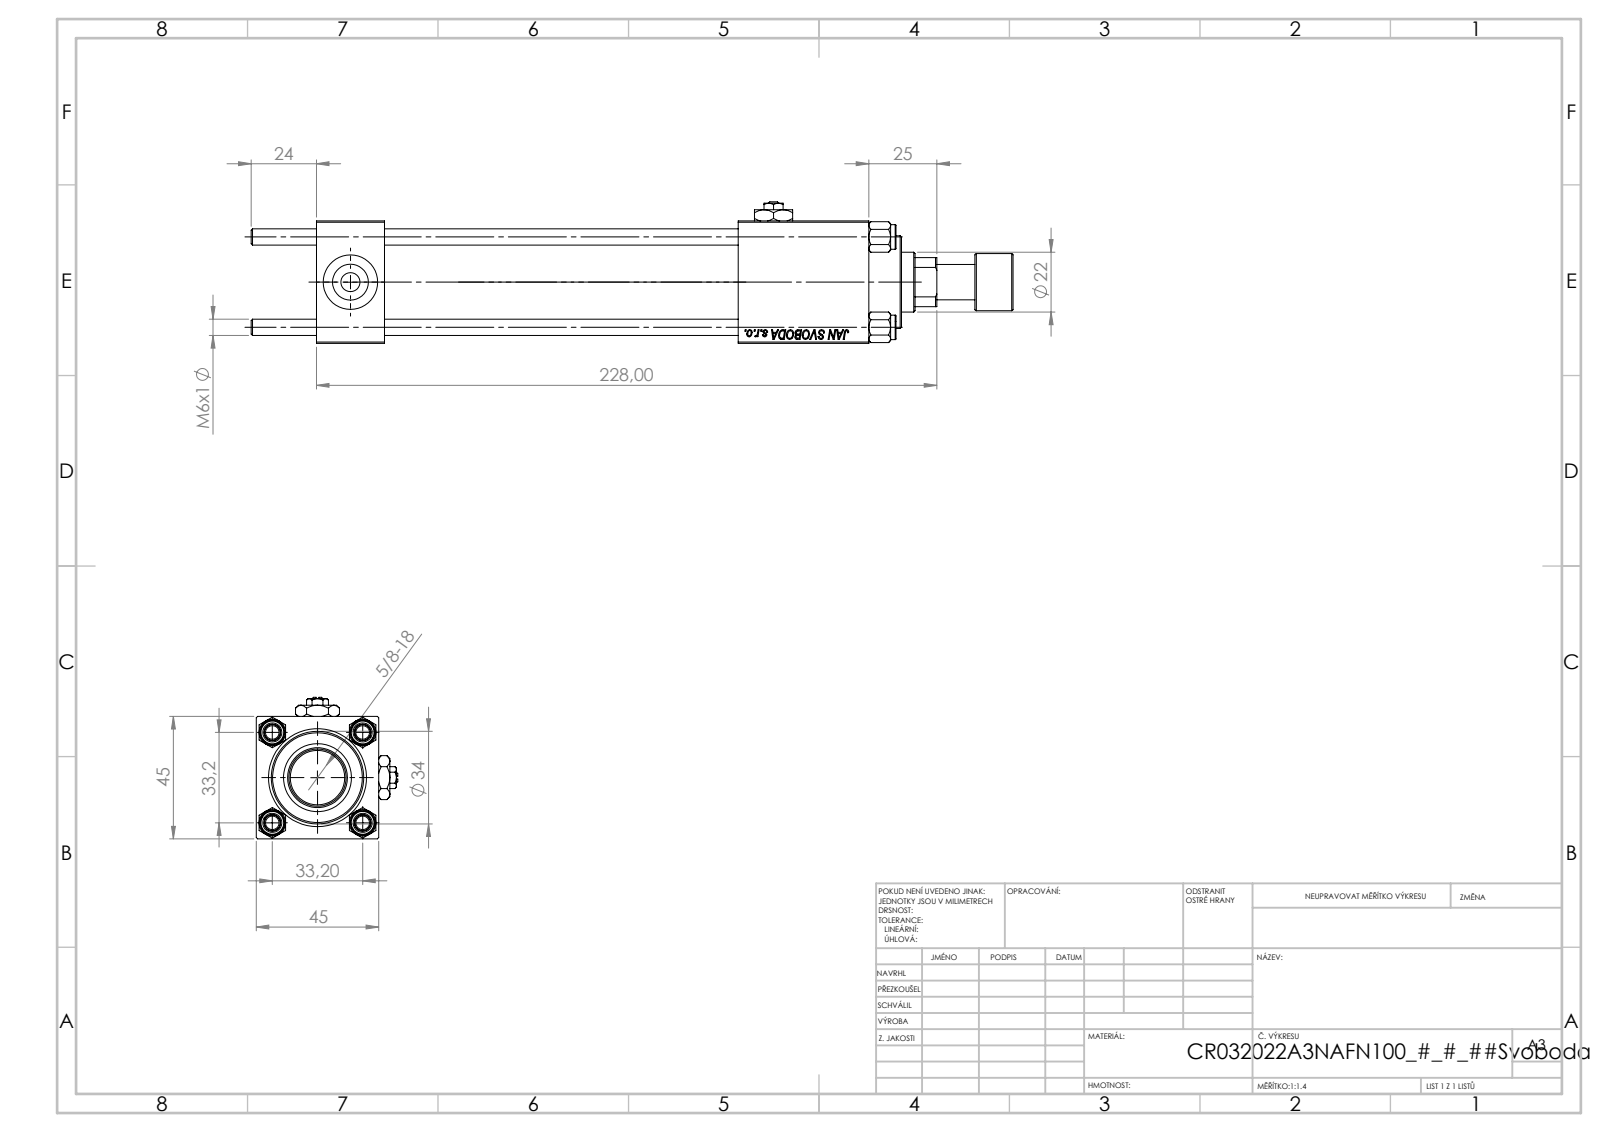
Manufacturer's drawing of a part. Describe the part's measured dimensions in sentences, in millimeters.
The part is named "Zatka_pro_OIL_PORT; V215CR_VCP; NUT_M5; V215CR_BODY_A (+3 more)". Its 3-D file was written by "SolidWorks 2019 (CONFIG_CONTROL_DESIGN)". It is 14 solids with 1243 faces: 567 planar, 94 cylindrical and 582 other. Overall it measures 280 by 52 by 52 millimeters. Its volume is 284 897 cubic millimeters and its surface area 110 248 square millimeters. Round holes: 4 of diameter 6, 2 of diameter 7, 2 of diameter 13.16, 2 of diameter 20, 1 of diameter 10.5, 1 of diameter 13, 1 of diameter 22, 1 of diameter 24, 1 of diameter 25, 1 of diameter 32, 1 of diameter 33. Round bosses or shafts: 4 of diameter 9, 1 of diameter 38, 1 of diameter 34, 1 of diameter 21, 1 of diameter 13. The main face-to-face distances are 45, 25, 203, 155, 130, 178, 48, 44.8, 174.3, 149.3. The hole center spacings are 23.48, 33.2, 46.95.
